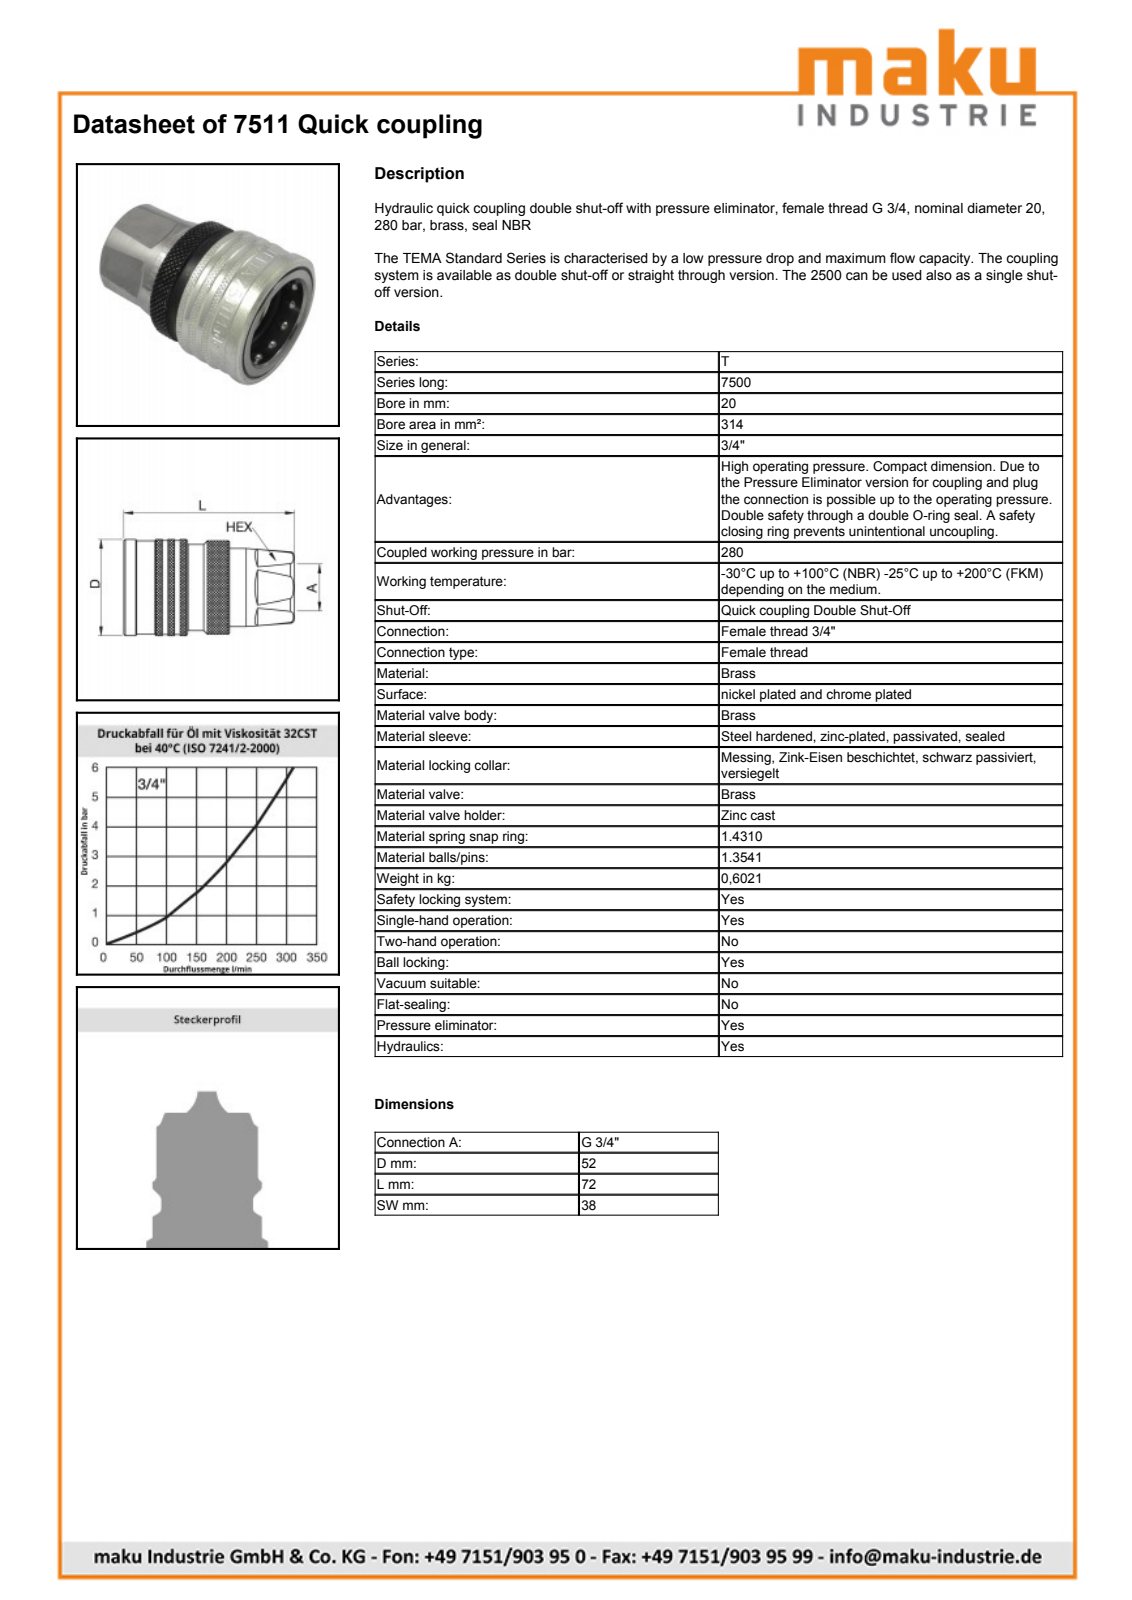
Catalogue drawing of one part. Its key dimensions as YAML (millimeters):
part_name: "7511"
step_written_by: "SolidWorks 2009 (AUTOMOTIVE_DESIGN)"
units: millimeters
bodies: {solids: 1, faces: 138, planar: 34, cylindrical: 44, other: 60}
overall_size: [73, 52, 52]
volume: 88172
surface_area: 21709
round_holes:
  - {diameter: 3.93, count: 1}
  - {diameter: 19, count: 1}
  - {diameter: 24.1, count: 1}
  - {diameter: 32.8, count: 1}
  - {diameter: 32.9, count: 1}
  - {diameter: 34.8, count: 1}
  - {diameter: 35.6, count: 1}
  - {diameter: 37.9, count: 1}
  - {diameter: 44.7, count: 1}
  - {diameter: 45.7, count: 1}
round_bosses_or_shafts:
  - {diameter: 52, count: 1}
  - {diameter: 51.2, count: 1}
  - {diameter: 51, count: 1}
  - {diameter: 49, count: 1}
  - {diameter: 46, count: 1}
  - {diameter: 45.6, count: 1}
  - {diameter: 43.5, count: 1}
  - {diameter: 41.5, count: 1}
face_to_face_distances: [38, 44, 18, 26, 73, 55, 29, 0.75, 44.75, 26.75]
